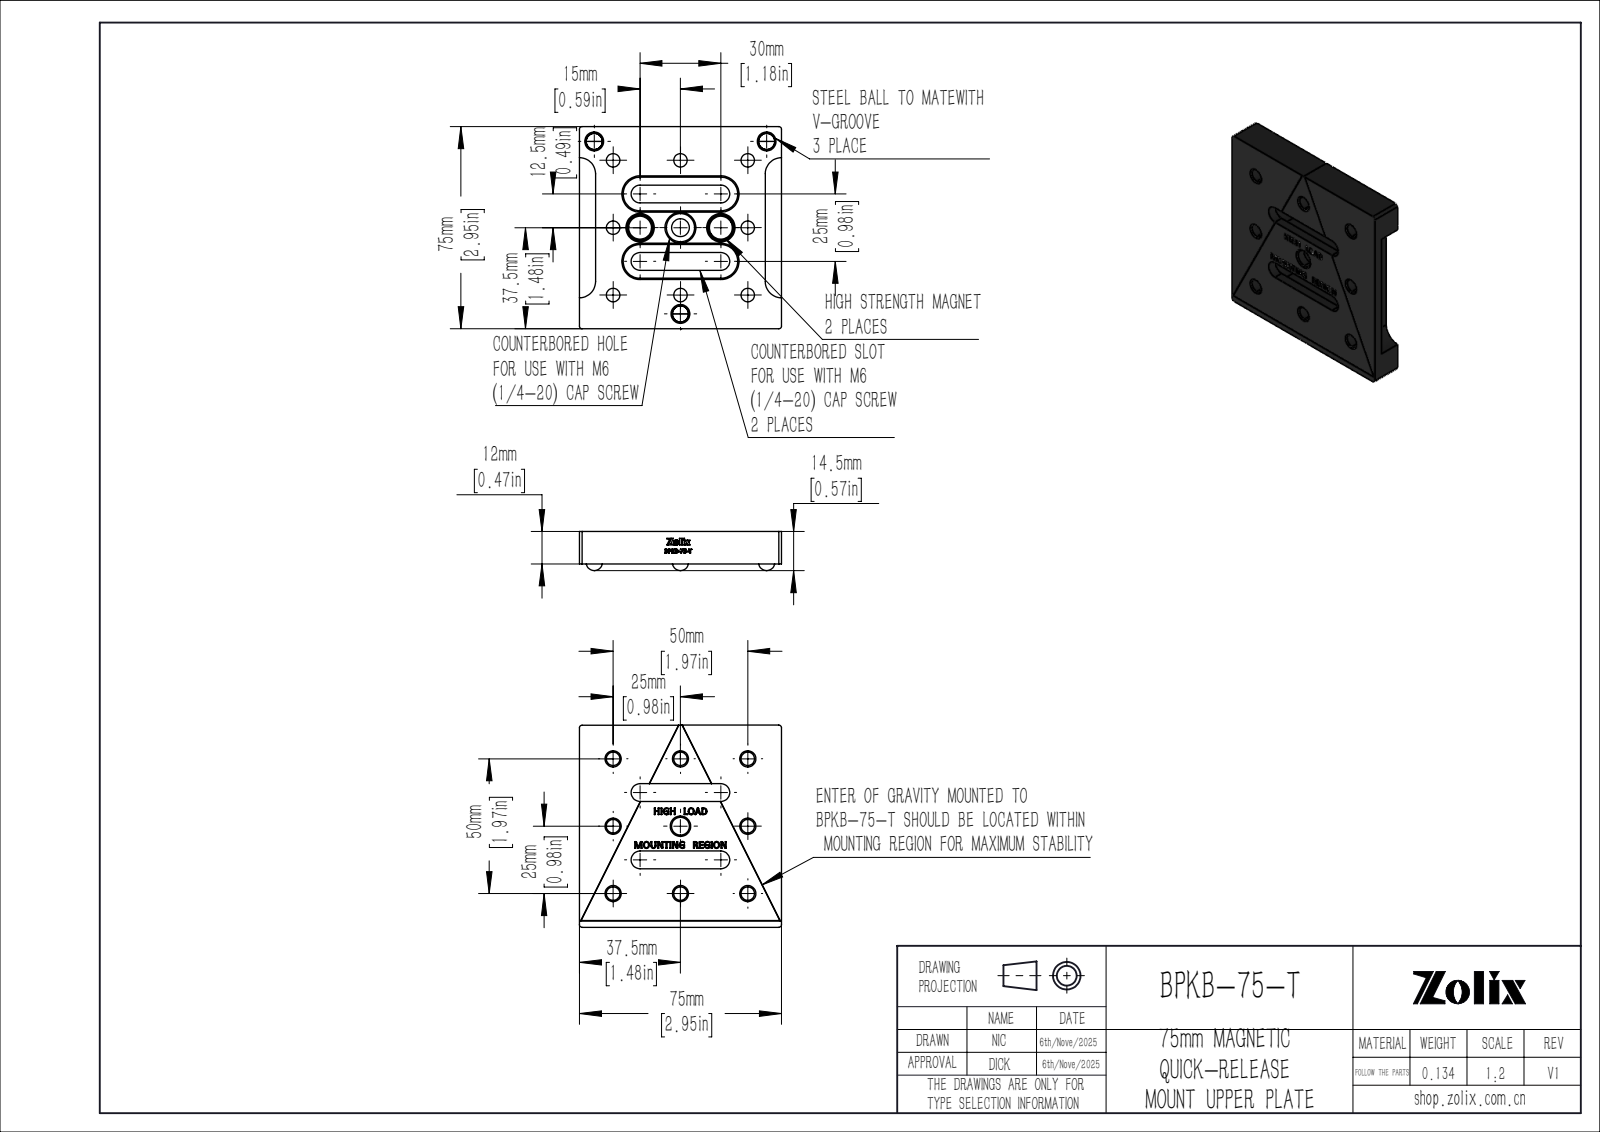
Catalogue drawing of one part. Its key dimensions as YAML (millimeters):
part_name: "BPKB-75-T"
step_written_by: "SolidWorks 2020 (CONFIG_CONTROL_DESIGN)"
units: millimeters
bodies: {solids: 6, faces: 801, planar: 432, cylindrical: 54, other: 315}
overall_size: [75.01, 75, 14.5]
volume: 49518
surface_area: 19290
round_holes:
  - {diameter: 5, count: 8}
  - {diameter: 6, count: 3}
  - {diameter: 3, count: 2}
  - {diameter: 9.55, count: 2}
  - {diameter: 6.6, count: 1}
  - {diameter: 10.5, count: 1}
round_bosses_or_shafts:
  - {diameter: 9.5, count: 2}
partial_cylinders:
  - {radius: 1, count: 4}
  - {radius: 3.3, count: 4}
  - {radius: 6, count: 4}
  - {radius: 6.25, count: 4}
face_to_face_distances: [12, 3.5, 8.5, 6, 69, 74.99, 75.01, 75, 25.01, 63]
hole_center_spacings: [25, 35.36, 55.91, 32.75, 57.43, 25.01, 50, 50.01]
